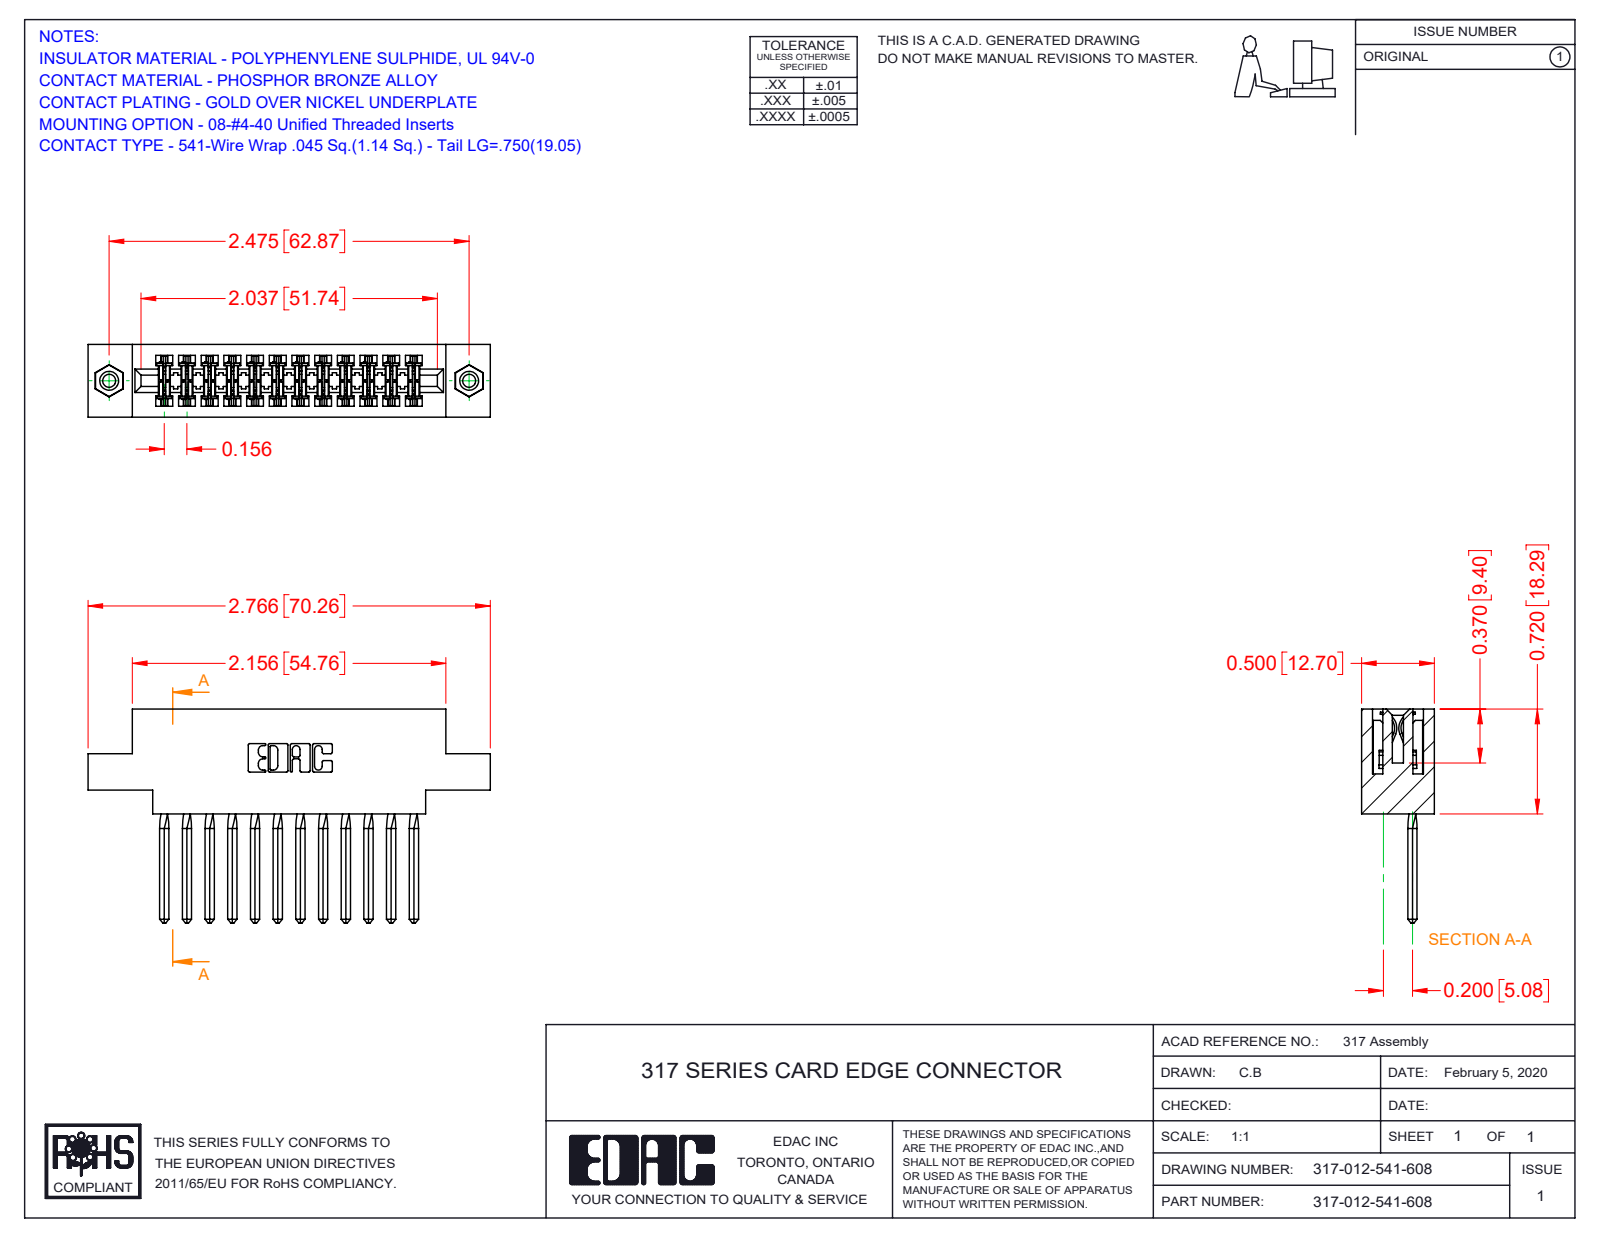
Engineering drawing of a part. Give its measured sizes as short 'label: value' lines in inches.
name: 317-290-002_541; 317-012-541-608; 317 Part_.156 Dia - TI; 345-250-001_345-250-003-102
written by: SolidWorks 2016 (CONFIG_CONTROL_DESIGN)
unit: in
bodies: 15 solids, 1986 faces (1578 planar, 344 cylindrical, 64 other)
size: 2.766 × 1.47 × 0.5
volume: 0.639 in³; area: 21.4 in²
holes: 2× ⌀0.089, 2× ⌀0.125, 2× ⌀0.156
bosses: 2× ⌀0.155
rounds: 24× R0.015, 22× R0.01, 6× R0.007, 6× R0.031, 3× R0.026, 2× R0.095, 2× R0.1, 2× R0.11
face distances: 0.5, 0.075, 0.425, 0.11, 0.22, 0.065, 0.35, 0.331, 0.195, 0.136
hole spacings: 2.475
